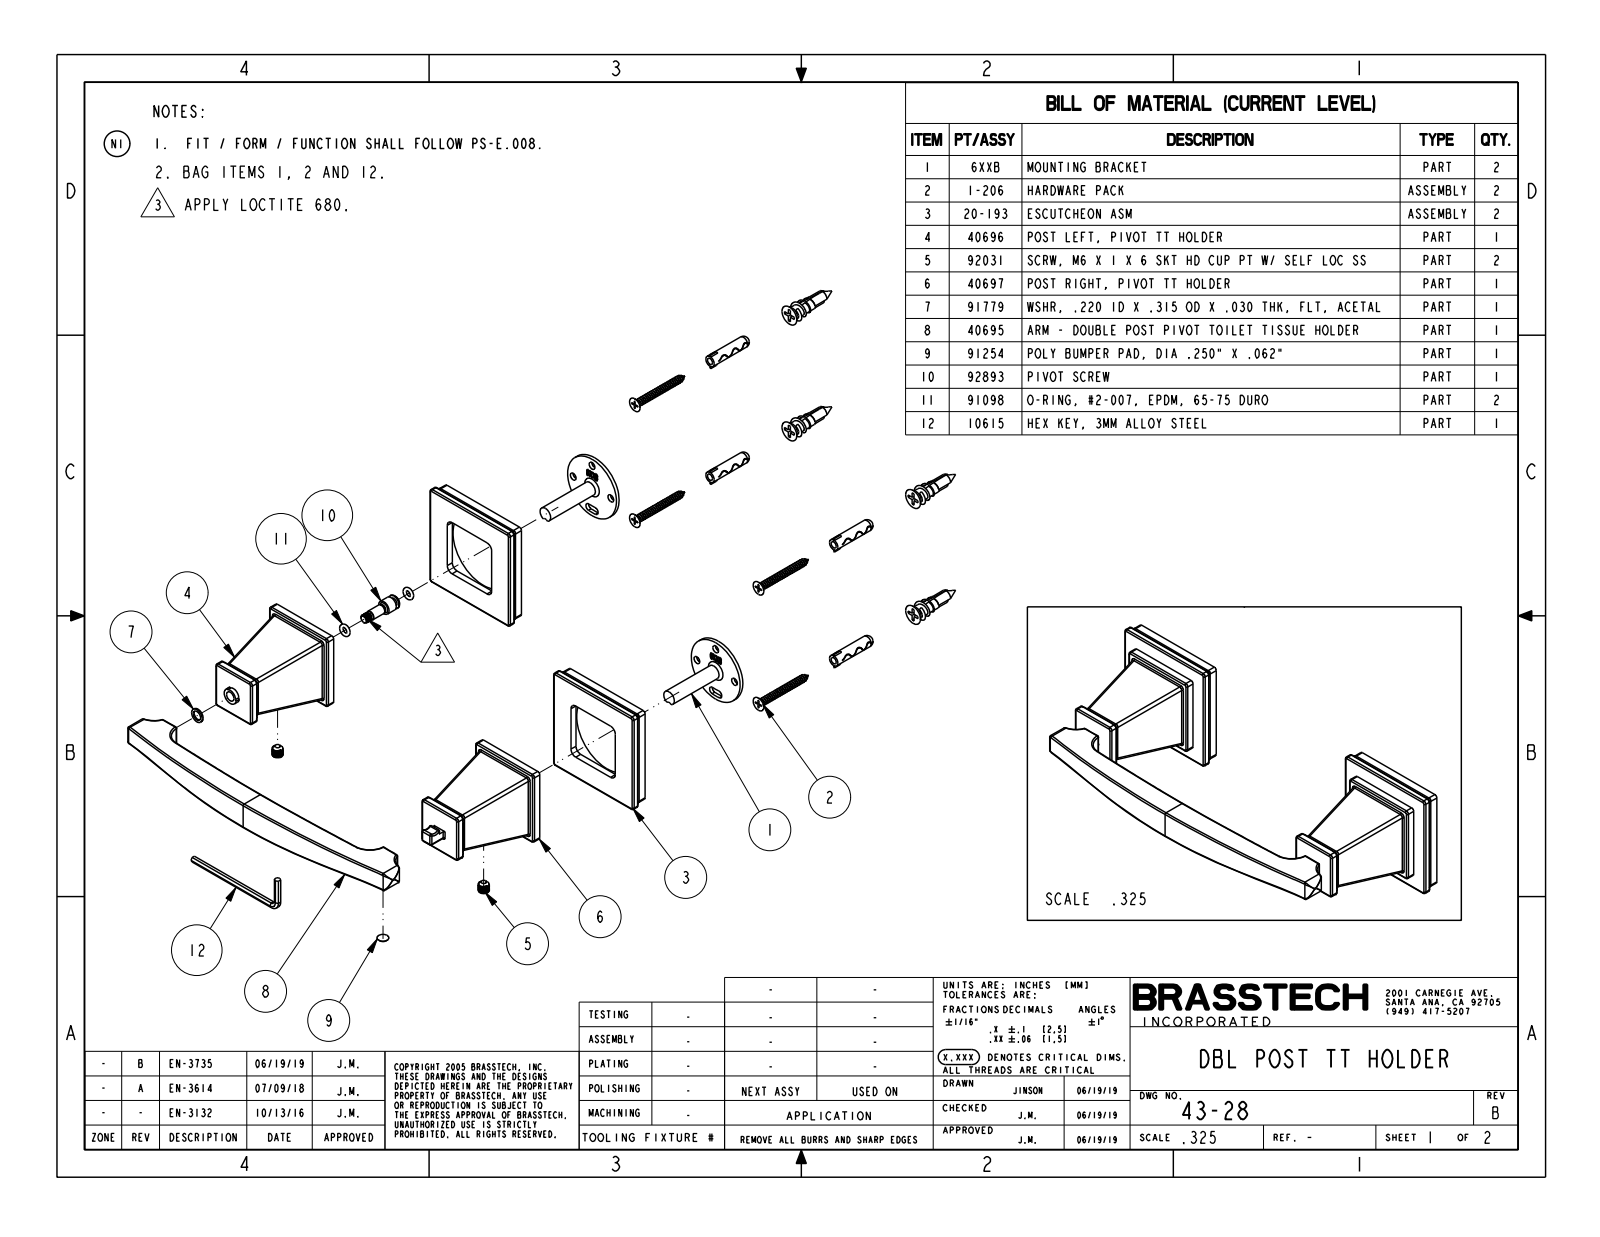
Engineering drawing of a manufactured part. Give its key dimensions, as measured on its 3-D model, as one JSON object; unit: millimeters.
{"part_name": "6XXB; 1-206_ASM; 12559; 91161 (+8 more)", "step_written_by": "PRO/ENGINEER BY PARAMETRIC TECHNOLOGY CORPORATION, 2014000 (CONFIG_CONTROL_DESIGN)", "units": "millimeters", "bodies": {"solids": 19, "faces": 1278, "planar": 433, "cylindrical": 446, "other": 399}, "overall_size": [228.3, 94.1, 60.7], "volume_mm3": 187100, "surface_area_mm2": 69290, "round_holes": [[4.3, 6], [6.6, 3], [5, 2], [8.2, 2], [45.8, 2], [47.1, 2], [55.2, 2], [2.3, 1], [3, 1], [3.2, 1], [3.4, 1], [7.1, 1]], "round_bosses_or_shafts": [[5.2, 8], [54.4, 2], [47.6, 2], [37.1, 2], [8, 2], [6, 2], [9.5, 1], [7, 1]], "partial_cylinders_radius": [[0.8, 56], [1.5, 40], [2.3, 12], [0.3, 10], [3.8, 10], [3.3, 8], [5.8, 8], [2.2, 4]], "face_to_face_distances": [10.4, 165.1, 5.6, 4.8, 2, 3.6, 8.4, 167.6, 6.9, 51.2], "hole_center_spacings": [14.3, 167.6, 20.2, 28.6, 153.3, 154, 168.2, 181.9]}
